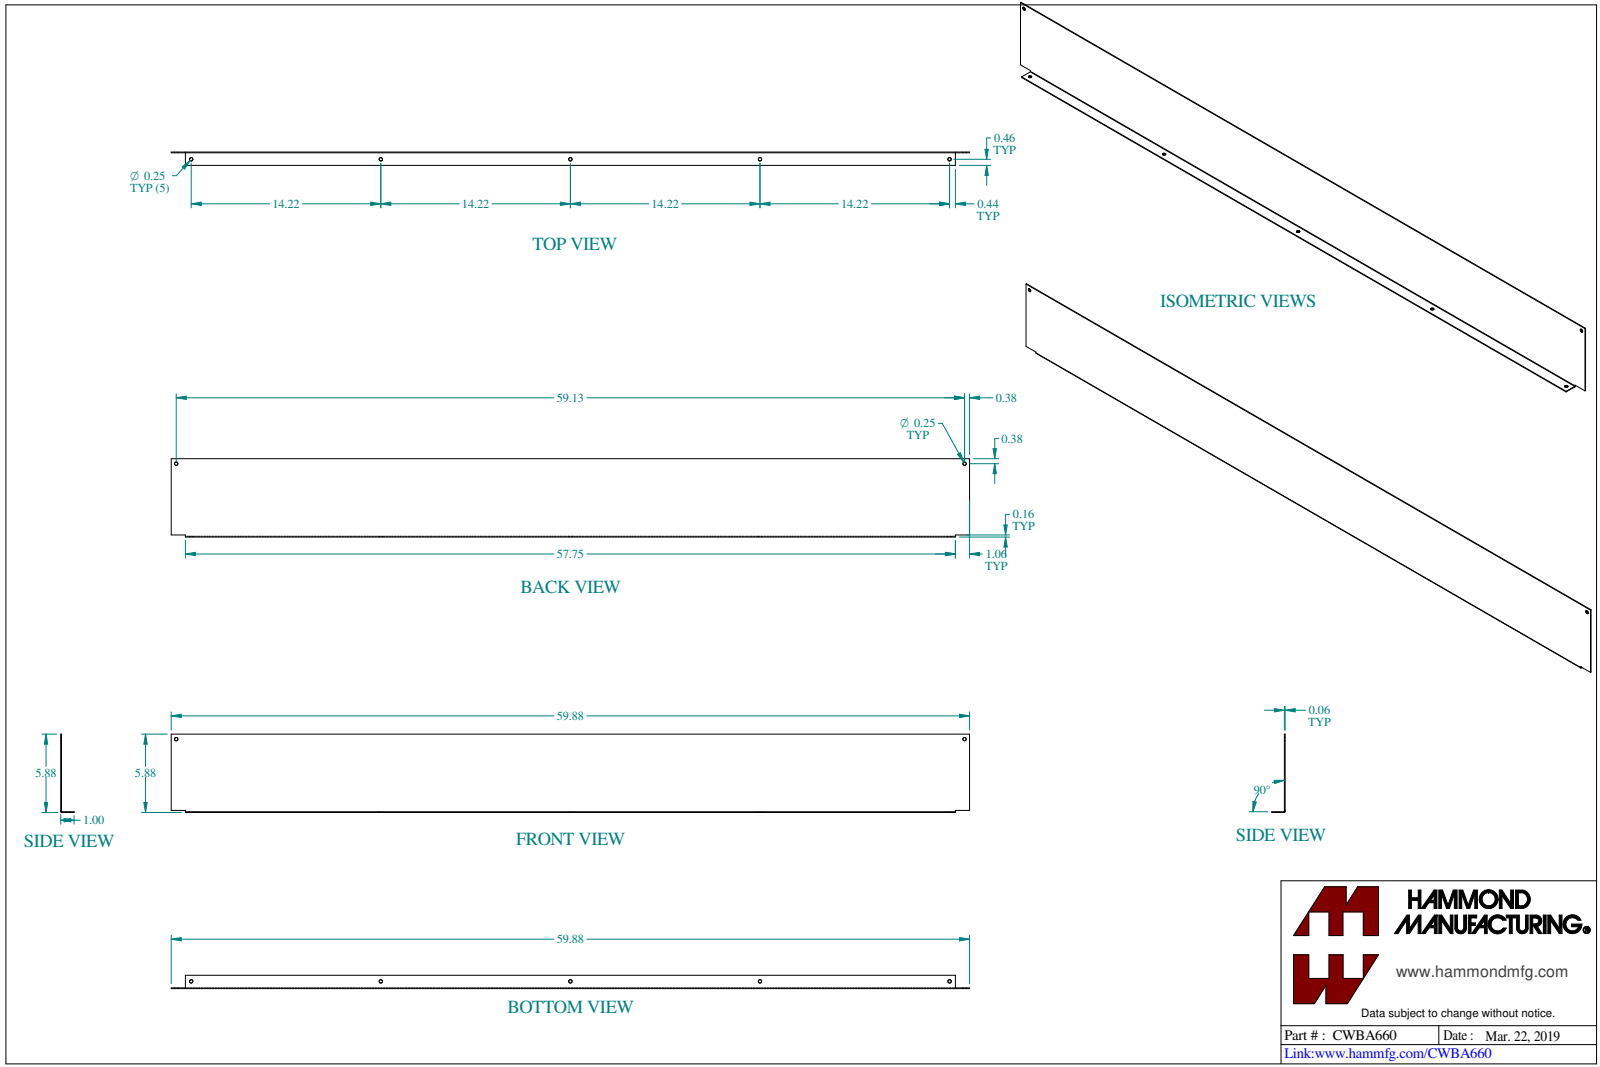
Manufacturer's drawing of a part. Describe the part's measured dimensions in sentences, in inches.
The part is named "CWBA660". Its 3-D file was written by "SolidWorks 2023 (CONFIG_CONTROL_DESIGN)". It is 3 solids with 63 faces: 35 planar, 22 cylindrical and 6 other. Overall it measures 59.875 by 6.318 by 1 inches. Its volume is 23.07 cubic inches and its surface area 817.2 square inches. Round holes: 7 of diameter 0.25, 1 of diameter 0.156. Round bosses or shafts: 1 of diameter 0.367, 1 of diameter 0.19. Partial cylindrical surfaces (rounded edges, fillets, slot ends): 1 of radius 0.029, 1 of radius 0.086. The main face-to-face distances are 0.057, 5.875, 5.818, 1, 0.943, 59.875, 1.063, 58.812, 0.156, 0.099. The hole center spacings are 14.219, 14.219, 28.437, 42.656, 28.438, 56.875, 59.125.
